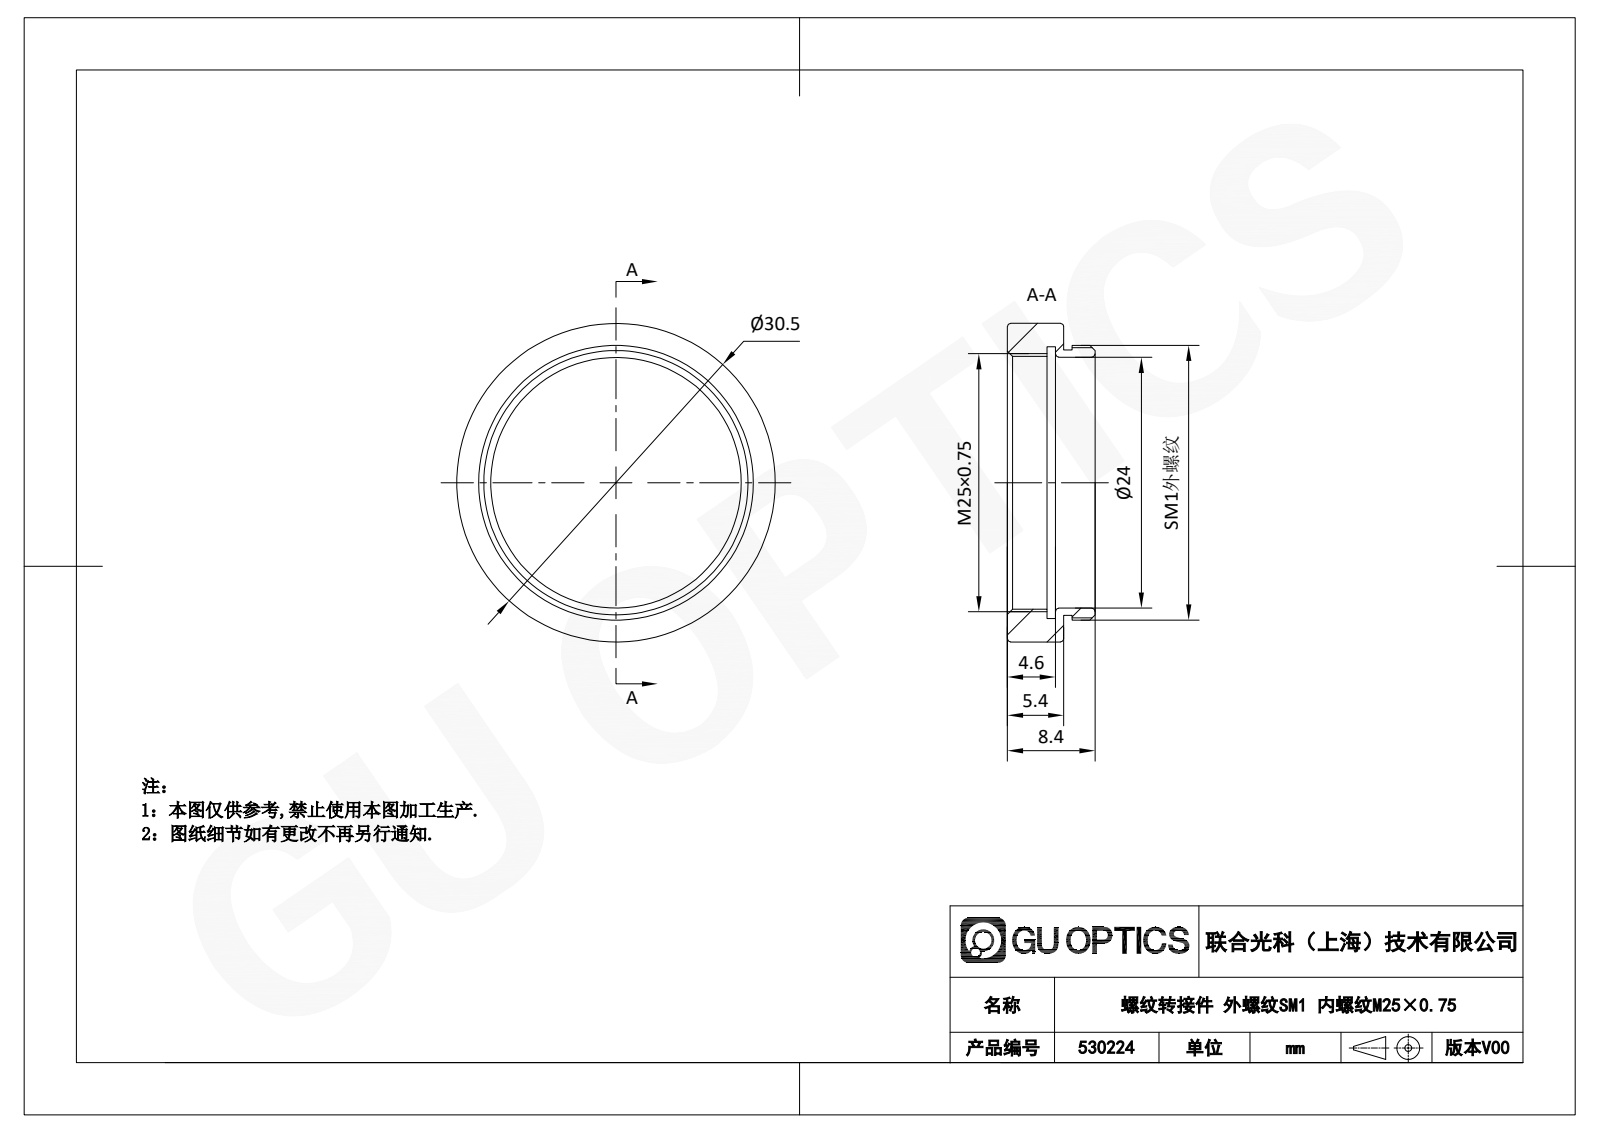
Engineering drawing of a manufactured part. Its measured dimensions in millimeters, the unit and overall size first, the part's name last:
Units: millimetres
Overall size (bounding box): 30.5 × 30.5 × 8.4
Round holes (diameter × count): ⌀24 ×1, ⌀24.2 ×1, ⌀26 ×1
Round bosses / shafts (diameter × count): ⌀30.5 ×1, ⌀26.29 ×1, ⌀25.4 ×1
Main face-to-face distances: 5.4, 0.8, 1.6, 3.8, 4.6, 2.4, 6.2, 2.2, 3, 8.4
Volume: 1 627 mm³ · Surface area: 2 084 mm²
Bodies: 1 solid, 18 faces (6 planar, 6 cylindrical, 6 other)
Part name (STEP PRODUCT): 530224
STEP written by: SolidWorks 2020 (CONFIG_CONTROL_DESIGN)
